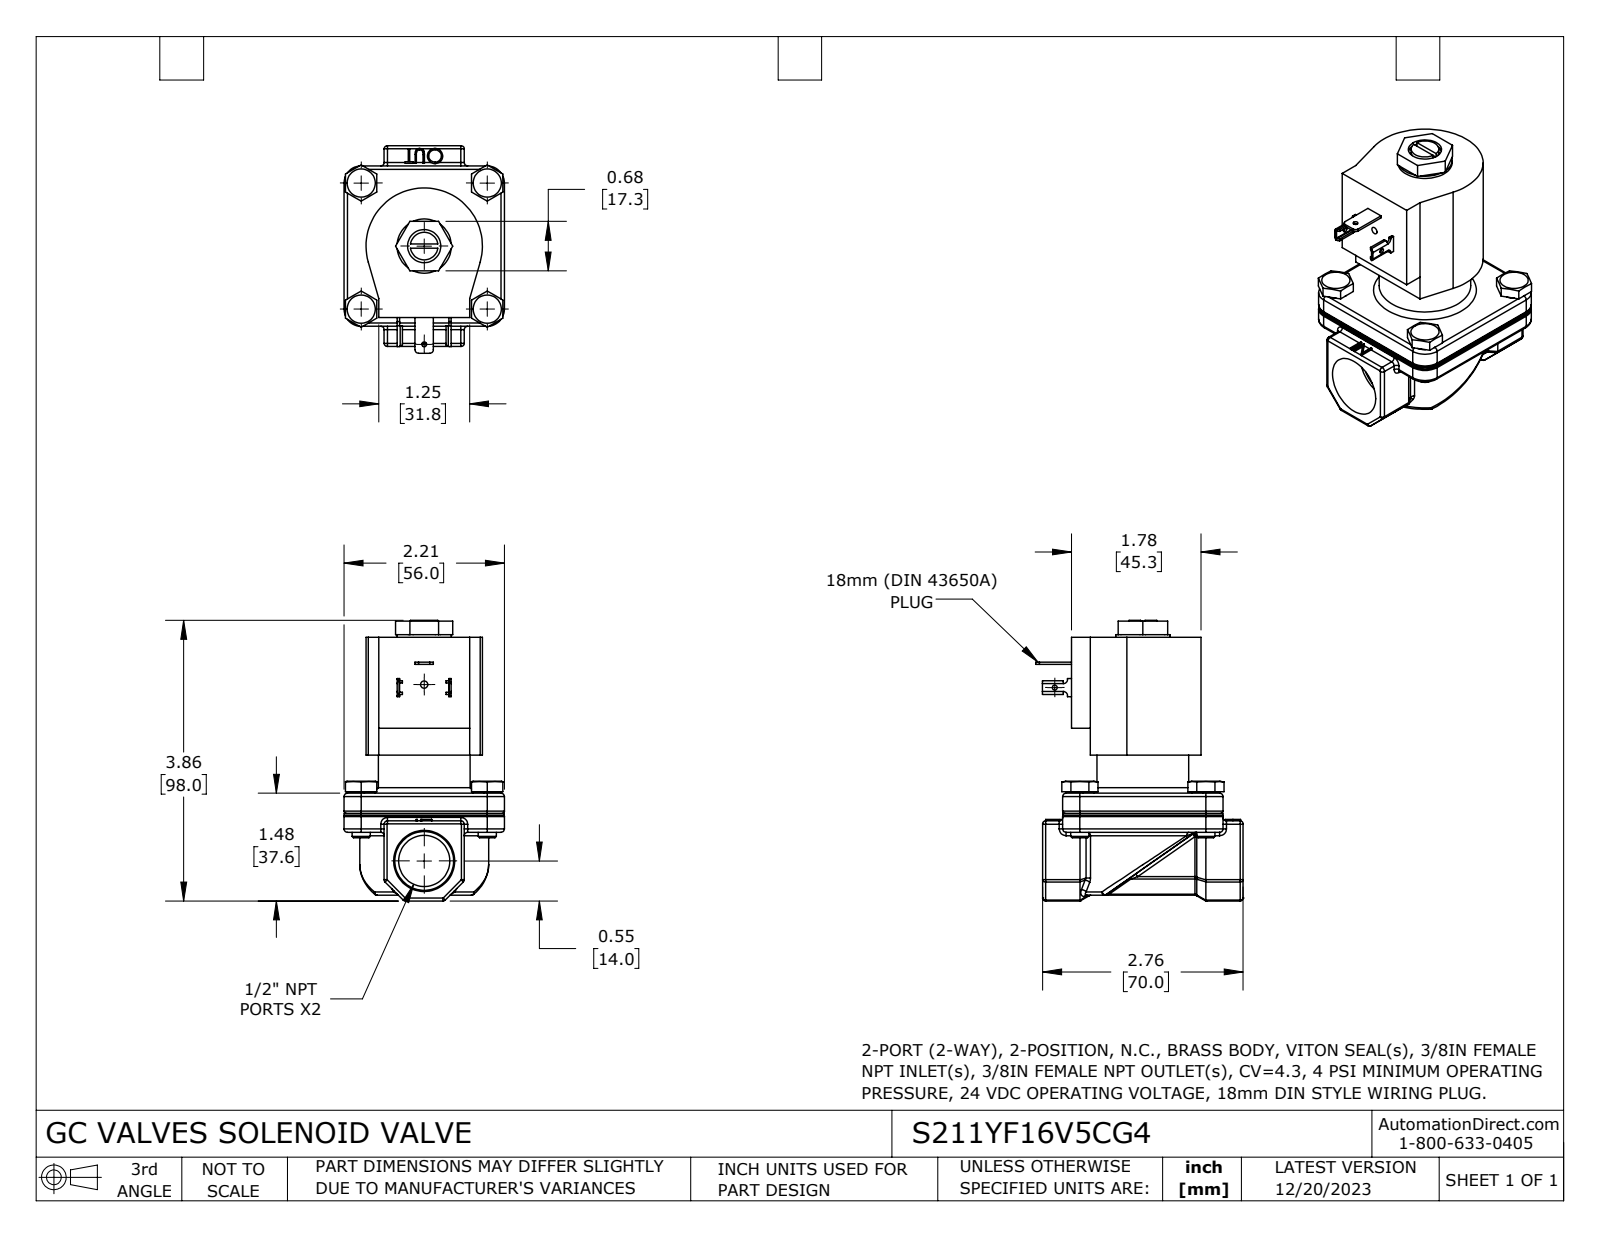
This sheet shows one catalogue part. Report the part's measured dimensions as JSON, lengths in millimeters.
{"part_name": "S211YF16V5CG4", "step_written_by": "SolidWorks 2023 (CONFIG_CONTROL_DESIGN)", "units": "millimeters", "bodies": {"solids": 1, "faces": 483, "planar": 204, "cylindrical": 153, "other": 126}, "overall_size": [98, 72.4, 56], "volume_mm3": 153000, "surface_area_mm2": 26930, "round_holes": [[1.7, 1], [1.7, 1], [2.5, 1], [11.6, 1], [17.9, 1]], "round_bosses_or_shafts": [[9.9, 4], [6.4, 4], [32, 1], [18.9, 1], [9.7, 1]], "partial_cylinders_radius": [[1.2, 57], [1, 12], [0.2, 4], [0.8, 4], [1, 4], [5.9, 4], [6, 4], [1.3, 2]], "face_to_face_distances": [54.4, 14, 42, 56, 13.6, 68.1, 7, 63, 26.9, 13.3], "hole_center_spacings": [34.3, 61.5]}
